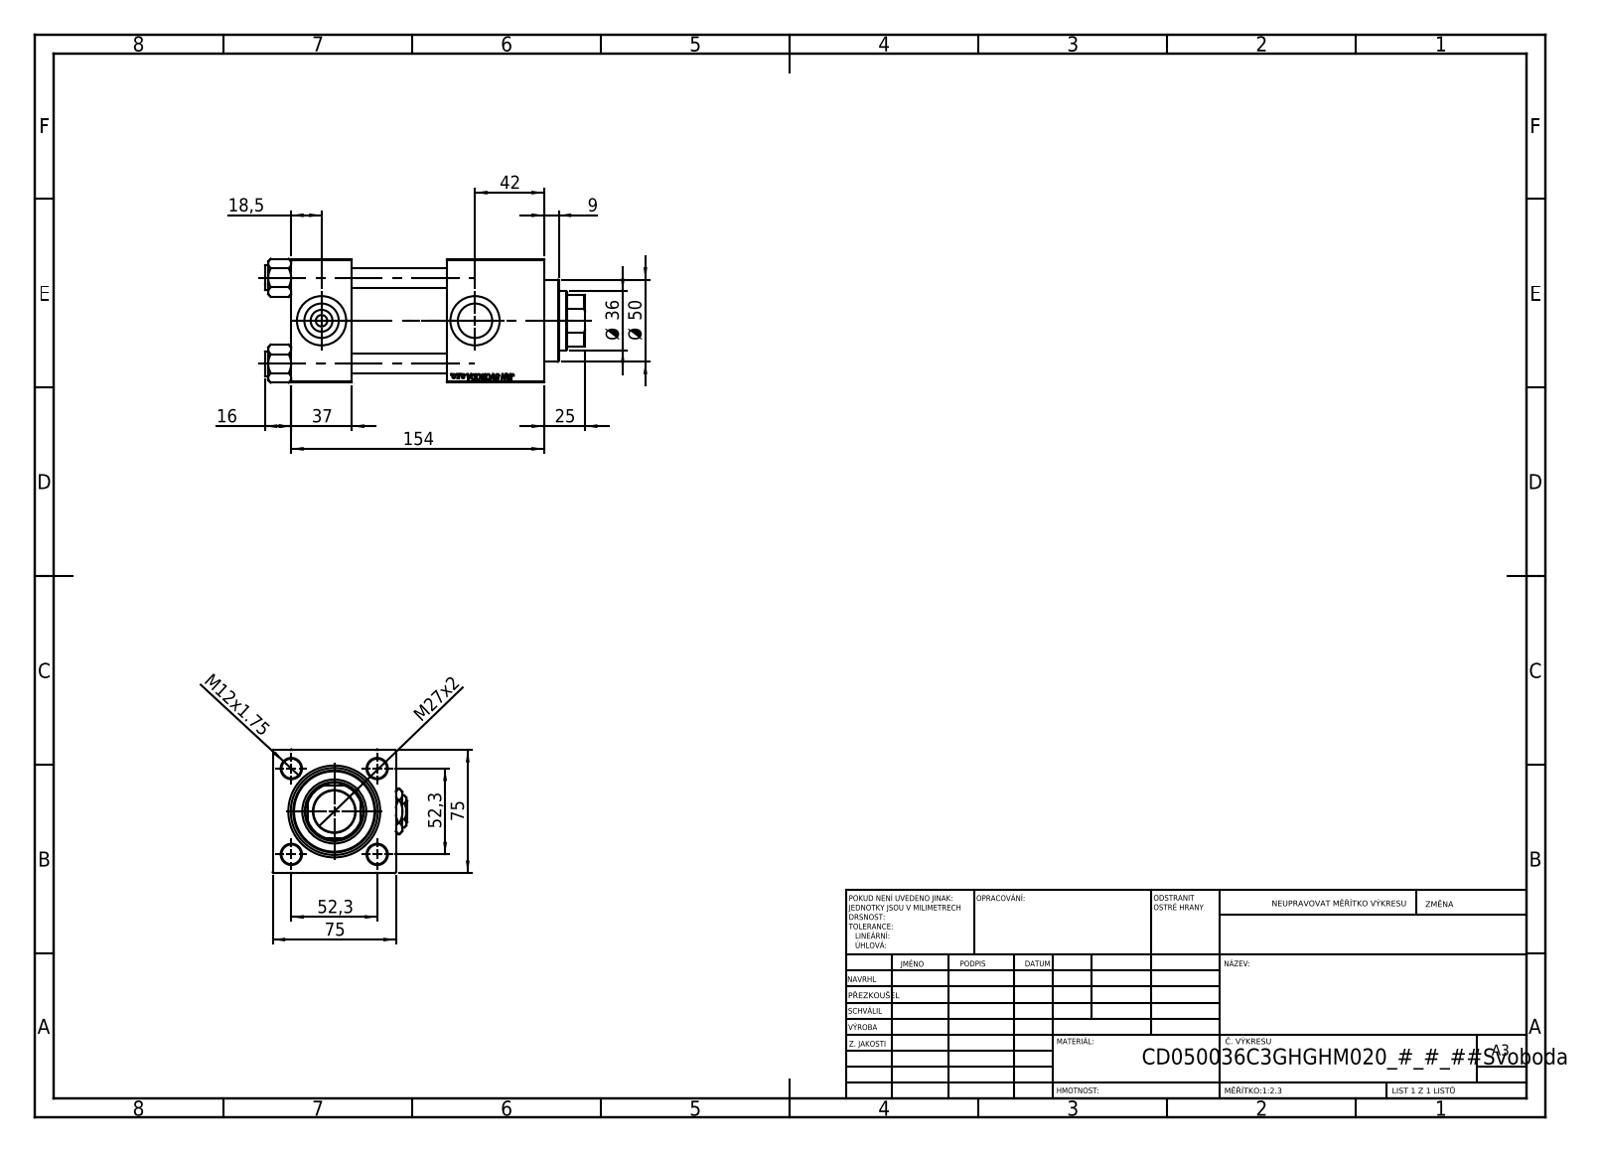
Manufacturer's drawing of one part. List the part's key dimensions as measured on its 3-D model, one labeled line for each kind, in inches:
Part name (STEP PRODUCT): V215CD_VCP_C; V215CD_Body_C; Zatka_pro_OIL_PORT; V215CD_VC_C (+2 more)
STEP written by: SolidWorks 2019 (CONFIG_CONTROL_DESIGN)
Units: inches
Bodies: 13 solids, 1249 faces (573 planar, 98 cylindrical, 578 other)
Overall size (bounding box): 7.677 × 3.228 × 2.974
Volume: 41.55 in³ · Surface area: 247.9 in²
Round holes (diameter × count): ⌀0.472 ×4, ⌀0.276 ×2, ⌀0.825 ×2, ⌀1.181 ×2, ⌀1.004 ×1, ⌀1.417 ×1, ⌀1.535 ×1, ⌀1.614 ×1, ⌀2.087 ×1
Round bosses / shafts (diameter × count): ⌀0.591 ×4, ⌀2.205 ×1, ⌀1.969 ×1
Partial cylindrical surfaces — rounded edges, fillets, slot ends (radius × count): R0.689 ×1
Main face-to-face distances: 2.953, 1.457, 3.74, 2.283, 2.323, 6.063, 4.606, 2.945, 4.933, 3.476
Hole centre spacings: 1.456, 2.059, 2.912, 3.681
